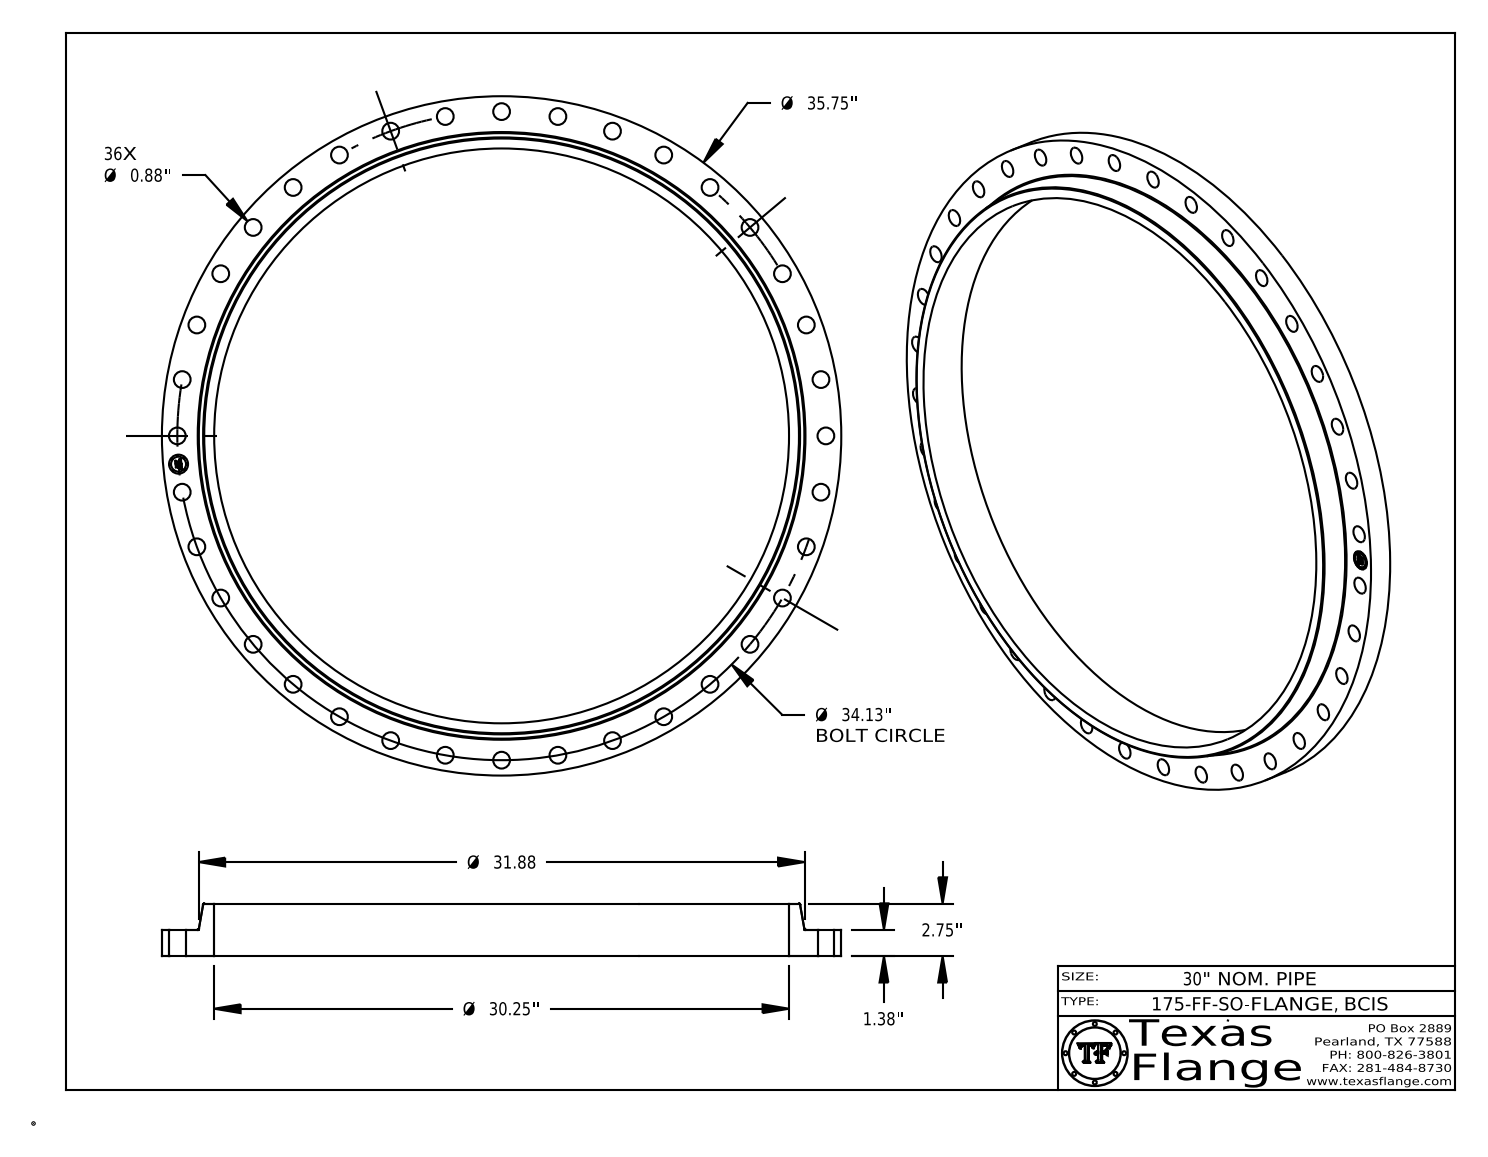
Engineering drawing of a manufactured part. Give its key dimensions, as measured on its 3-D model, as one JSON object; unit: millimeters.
{"part_name": "BCIS, Class 175-FF-SO", "step_written_by": "CATIA V5 STEP AP214 (AUTOMOTIVE_DESIGN)", "units": "millimeters", "bodies": {"solids": 1, "faces": 470, "planar": 368, "cylindrical": 96, "other": 6}, "overall_size": [908.1, 908.1, 69.9], "volume_mm3": 7468000, "surface_area_mm2": 768400, "round_holes": [[22.4, 36], [25.4, 1], [768.4, 1]], "round_bosses_or_shafts": [[1.5, 8], [908.1, 1], [20, 1]], "face_to_face_distances": [35.1, 69.9, 34.8, 34.7, 0.4, 35.2, 7.6, 7.4, 1.4, 4.9], "hole_center_spacings": [433.5, 863.6, 75.6, 750.7, 224.4, 150.5, 664.1, 785.7]}
